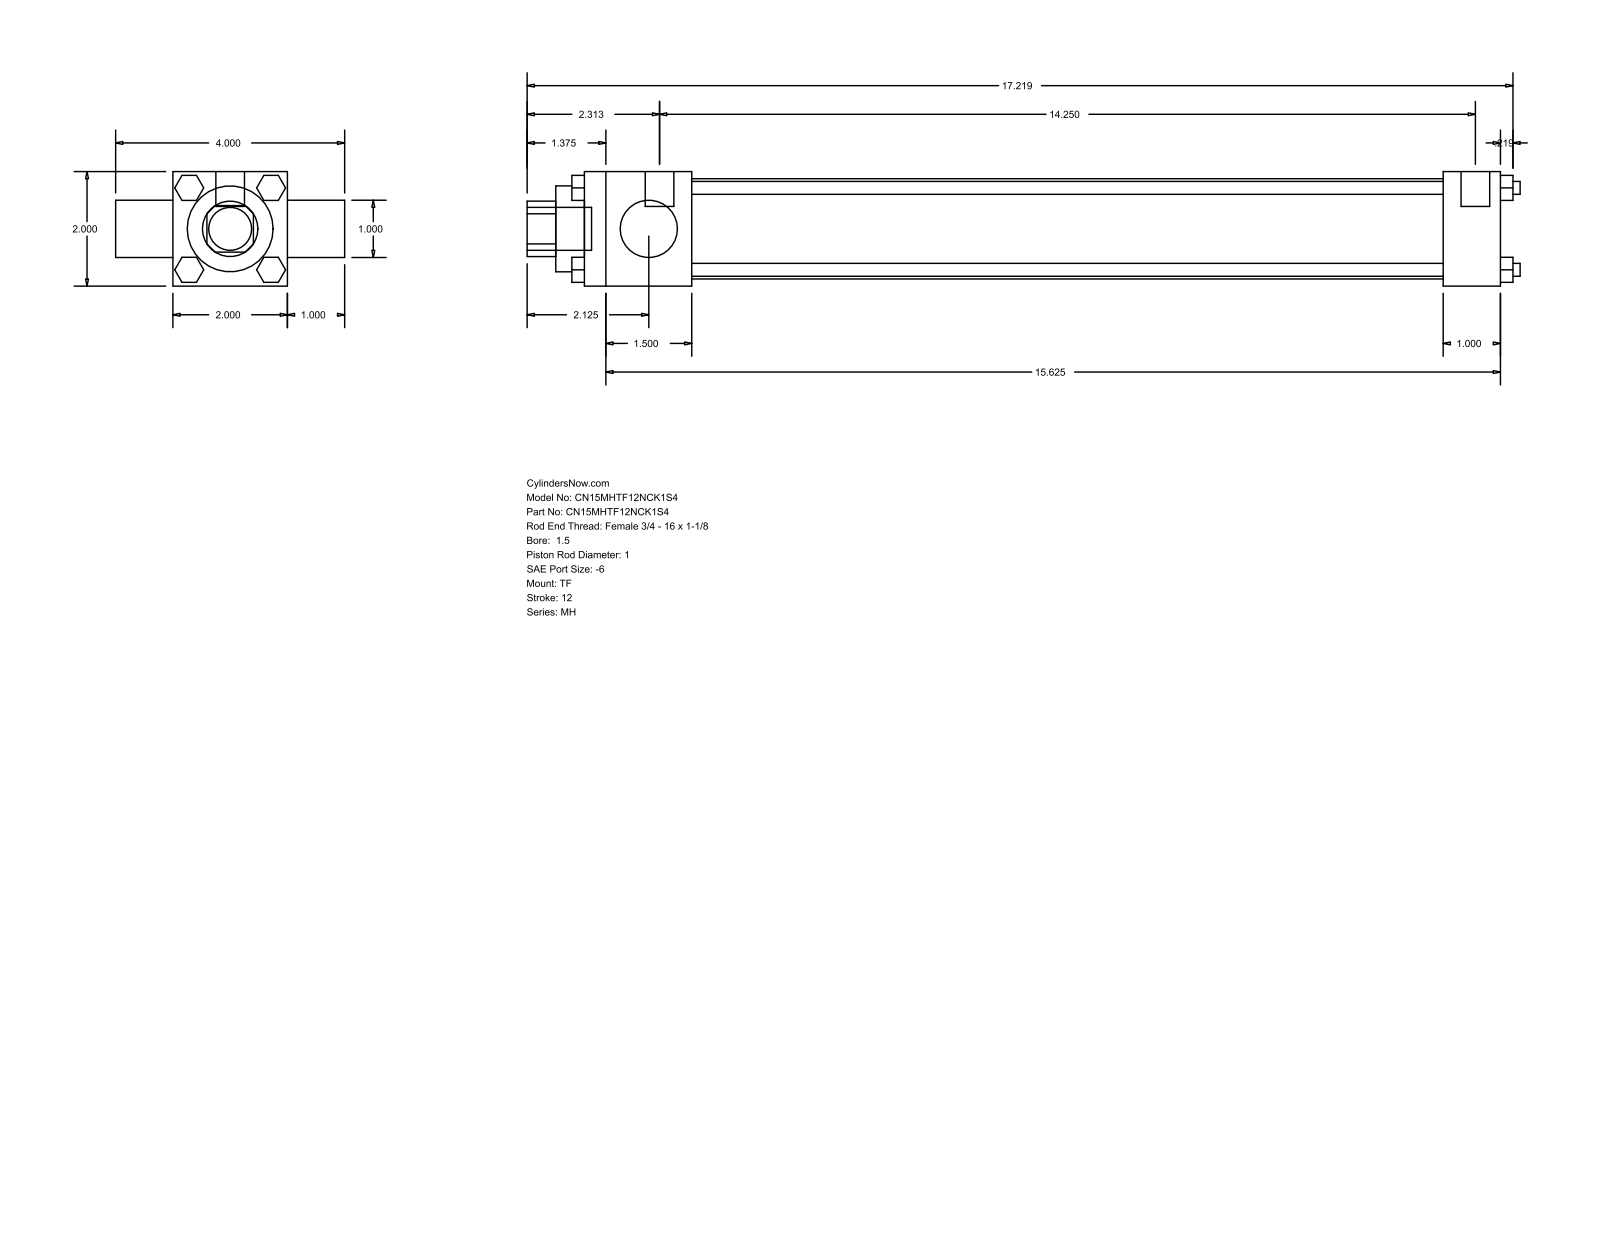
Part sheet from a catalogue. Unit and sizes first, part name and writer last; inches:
Units: inches
Overall size (bounding box): 17.344 × 4 × 2
Round holes (diameter × count): ⌀1 ×2, ⌀1.5 ×1, ⌀1.75 ×1
Round bosses / shafts (diameter × count): ⌀0.225 ×4, ⌀0.219 ×3, ⌀0.5 ×2, ⌀0.75 ×1
Partial cylindrical surfaces — rounded edges, fillets, slot ends (radius × count): R0.484 ×1
Main face-to-face distances: 2, 1, 16, 3, 1.875, 14.125, 15, 13.125, 16.219, 0.5
Bodies: 0 solids, 120 faces (92 planar, 28 cylindrical, 0 other)
Part name (STEP PRODUCT): MH_TF__0150_1
STEP written by: GSSL Pune (CONFIG_CONTROL_DESIGN)
